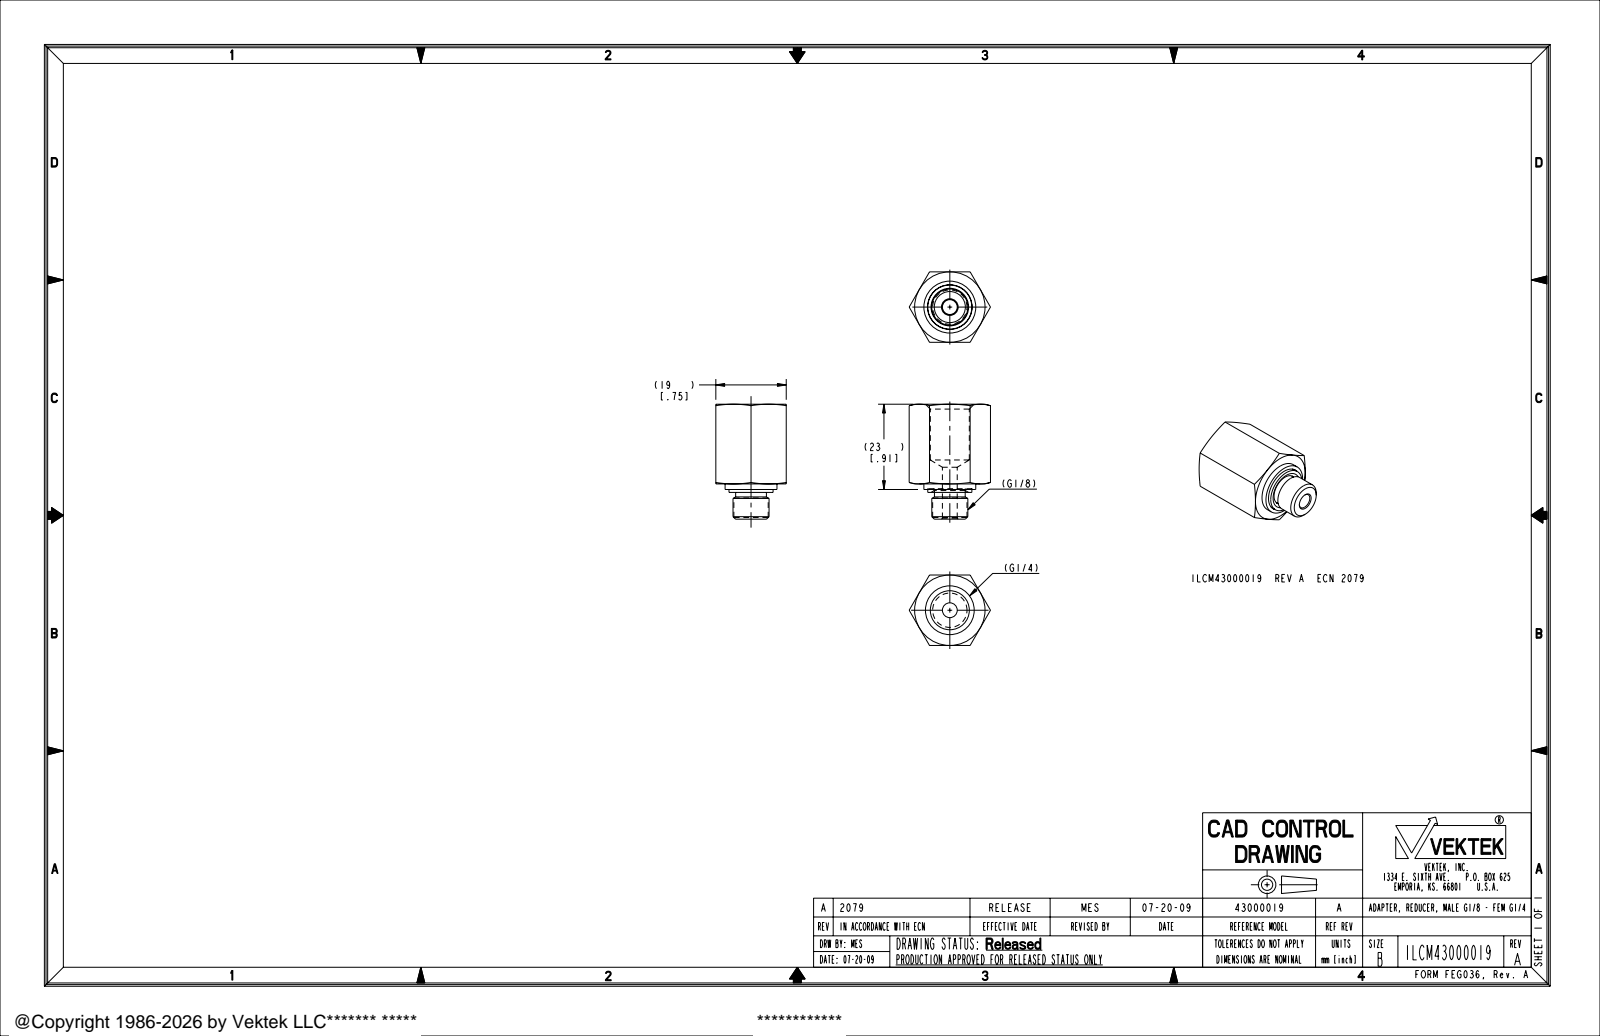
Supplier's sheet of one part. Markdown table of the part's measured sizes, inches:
| quantity | value |
| --- | --- |
| part name | ILCM43000019 |
| STEP written by | PRO/ENGINEER BY PARAMETRIC TECHNOLOGY CORPORATION, 2007460 (AUTOMOTIVE_DESIGN_CC2) |
| units | inches |
| bodies | 1 solid, 55 faces (13 planar, 18 cylindrical, 24 other) |
| overall size | 1.22 × 0.864 × 0.748 |
| volume | 0.361 in³ |
| surface area | 4.962 in² |
| round holes (diameter × count) | 0.157 × 1, 0.331 × 1, 0.414 × 1, 0.474 × 1 |
| round bosses / shafts (diameter × count) | 0.551 × 1, 0.469 × 1, 0.383 × 1, 0.365 × 1, 0.327 × 1 |
| main face-to-face distances | 0.748, 0.846, 0.059, 0.906, 0.315, 0.374, 1.22, 0.284, 0.031, 0.09 |
